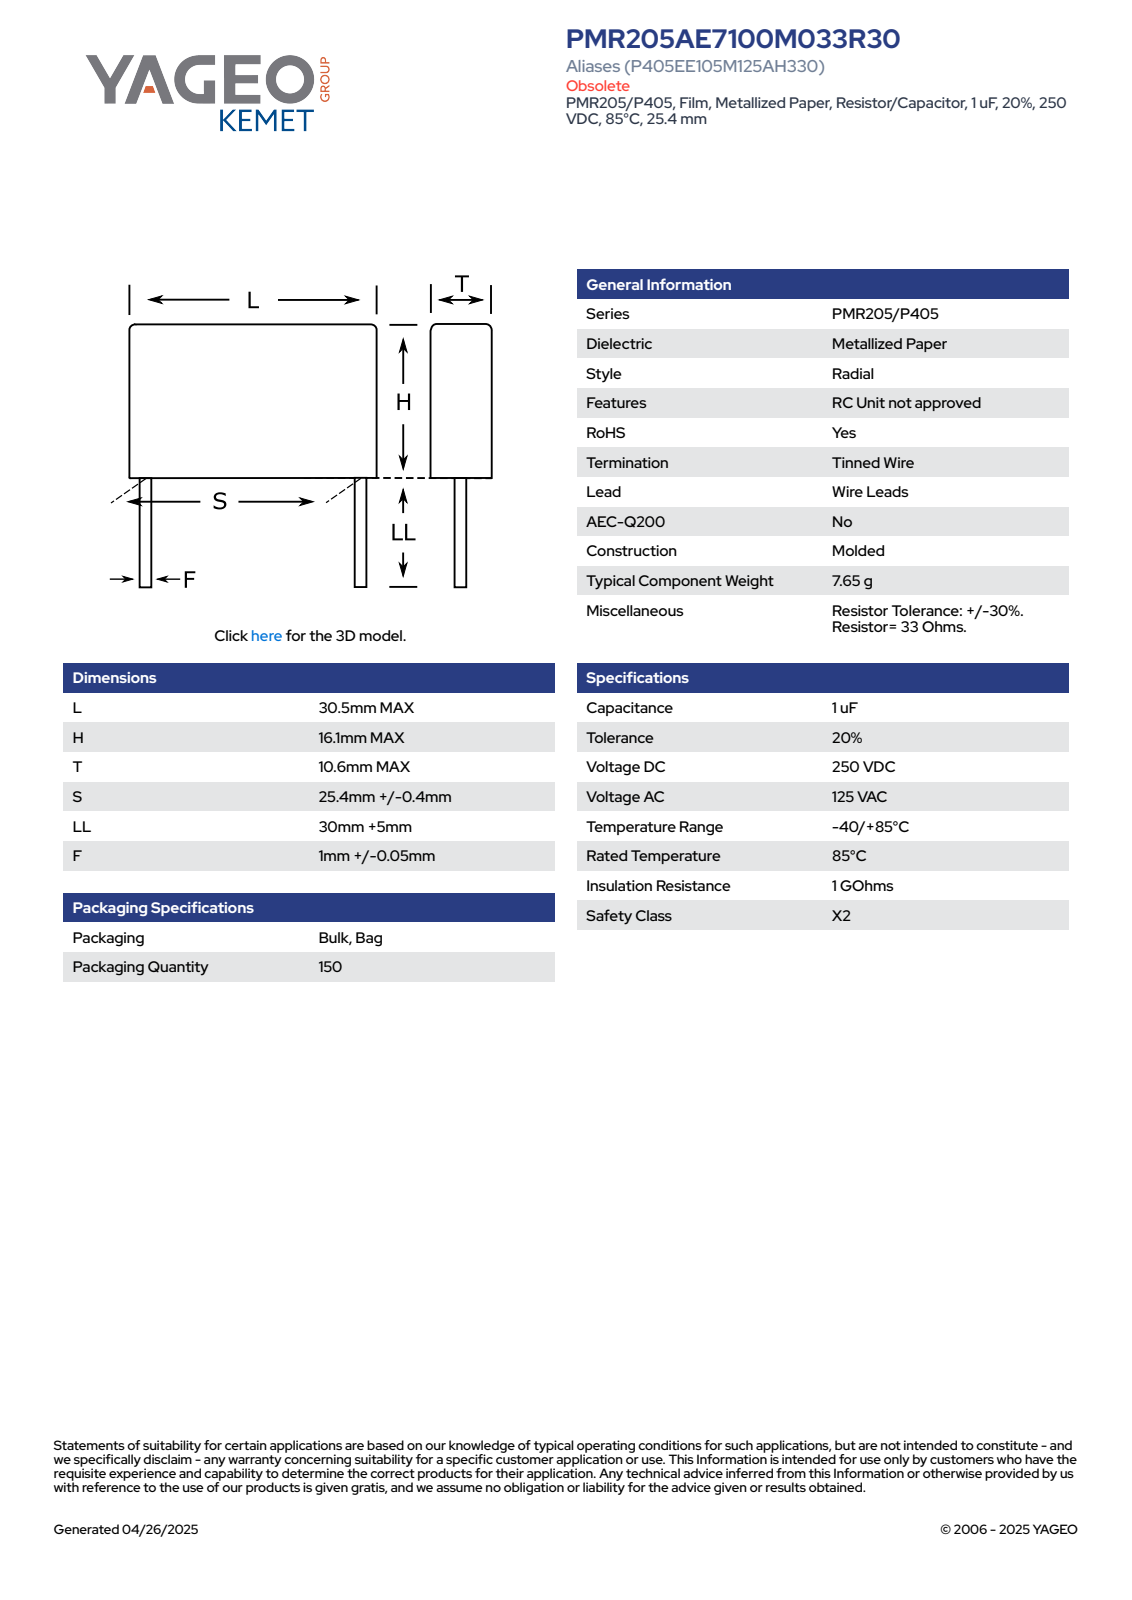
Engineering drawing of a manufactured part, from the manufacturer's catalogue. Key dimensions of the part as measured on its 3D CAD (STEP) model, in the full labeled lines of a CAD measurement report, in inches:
Part name (STEP PRODUCT): CFR_MOLDED_30.5X16.1X10.6_L30.5H16.1T10.6S25.4LL35F1.05
STEP written by: SolidWorks 2014 (AUTOMOTIVE_DESIGN)
Units: inches
Bodies: 4 solids, 73 faces (65 planar, 8 cylindrical, 0 other)
Overall size (bounding box): 2.012 × 1.201 × 0.418
Volume: 0.321 in³ · Surface area: 3.453 in²
Round bosses / shafts (diameter × count): ⌀0.041 ×2
Partial cylindrical surfaces — rounded edges, fillets, slot ends (radius × count): R0.02 ×4
Main face-to-face distances: 0.417, 0.634, 1.201, 0.418, 1.378, 2.012, 1.751, 0.373, 0.261, 1.644
